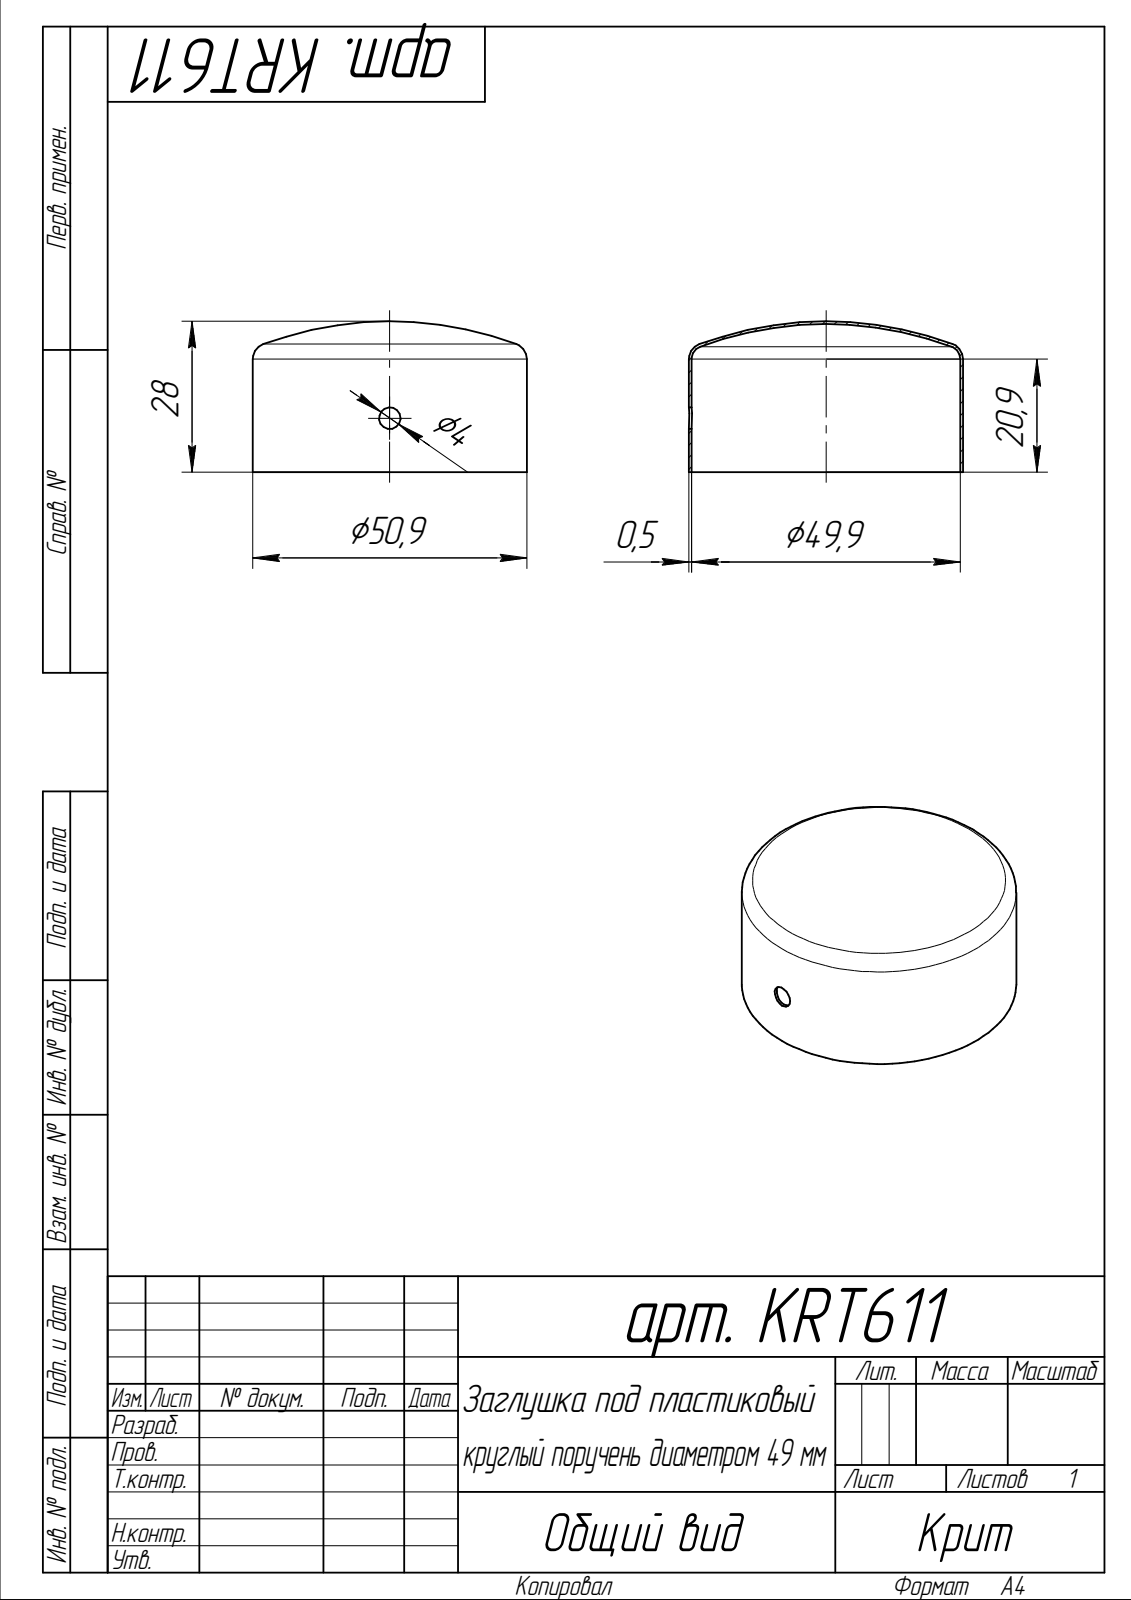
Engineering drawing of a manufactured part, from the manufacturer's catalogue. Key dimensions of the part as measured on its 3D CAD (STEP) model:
Part name (STEP PRODUCT): арт. KRT611
STEP written by: SolidWorks 2014 (AUTOMOTIVE_DESIGN)
Units: millimetres
Bodies: 1 solid, 15 faces (1 planar, 6 cylindrical, 8 other)
Overall size (bounding box): 50.9 × 50.9 × 28
Volume: 2 797 mm³ · Surface area: 11 275 mm²
Round holes (diameter × count): ⌀4 ×1, ⌀49.9 ×1
Round bosses / shafts (diameter × count): ⌀50.9 ×1
